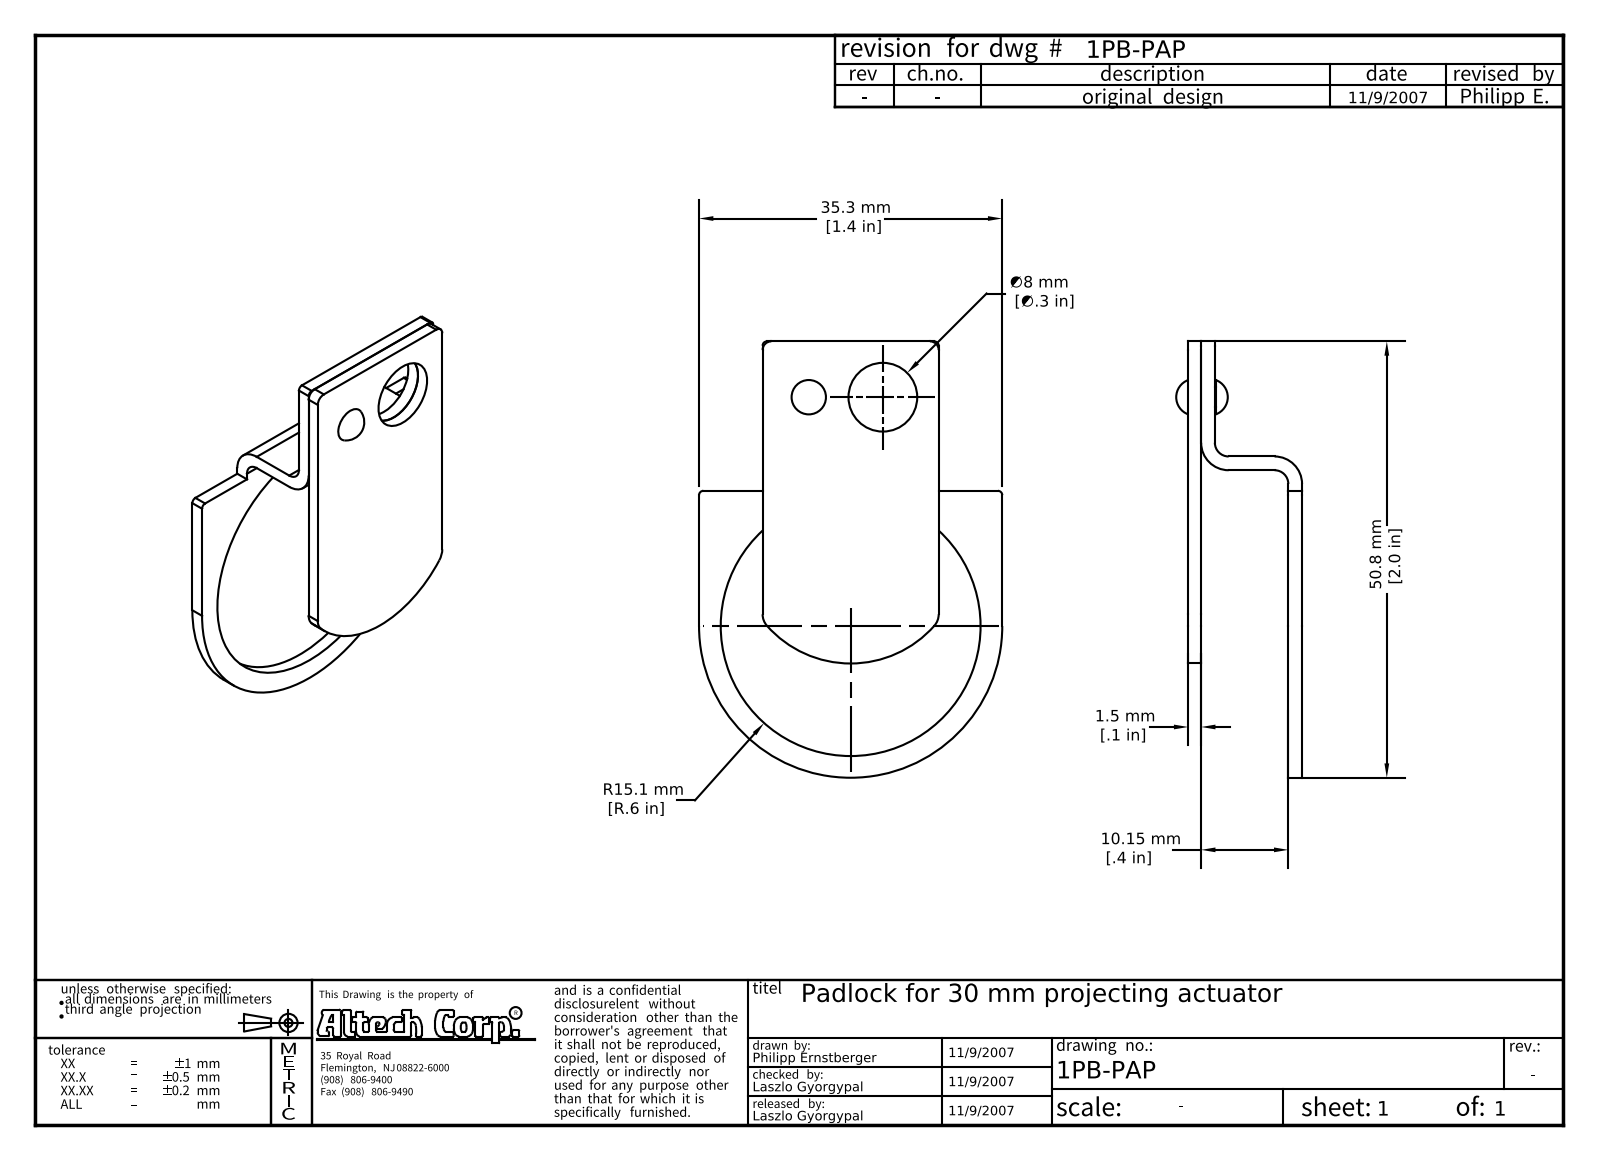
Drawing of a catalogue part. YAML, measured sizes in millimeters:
part_name: "PAP; standoff; top; SS 1440 - KN 2.3 x 18 x 3"
step_written_by: "Autodesk Inventor 2008 (AUTOMOTIVE_DESIGN)"
units: millimeters
bodies: {solids: 3, faces: 45, planar: 23, cylindrical: 20, other: 2}
overall_size: [50.8, 35.3, 14.65]
volume: 2332
surface_area: 3731
round_holes:
  - {diameter: 2.5, count: 1}
  - {diameter: 8, count: 1}
  - {diameter: 30.25, count: 1}
round_bosses_or_shafts:
  - {diameter: 2.3, count: 1}
partial_cylinders:
  - {radius: 0.5, count: 4}
  - {radius: 1, count: 2}
  - {radius: 1.6, count: 2}
  - {radius: 2, count: 2}
  - {radius: 3.2, count: 2}
  - {radius: 13, count: 1}
  - {radius: 17.65, count: 1}
face_to_face_distances: [1.5, 1.6, 10.15, 11.65, 11.75, 13.25, 8.55, 3.1, 20.5, 15]
hole_center_spacings: [8.63, 26.91, 27.09]
